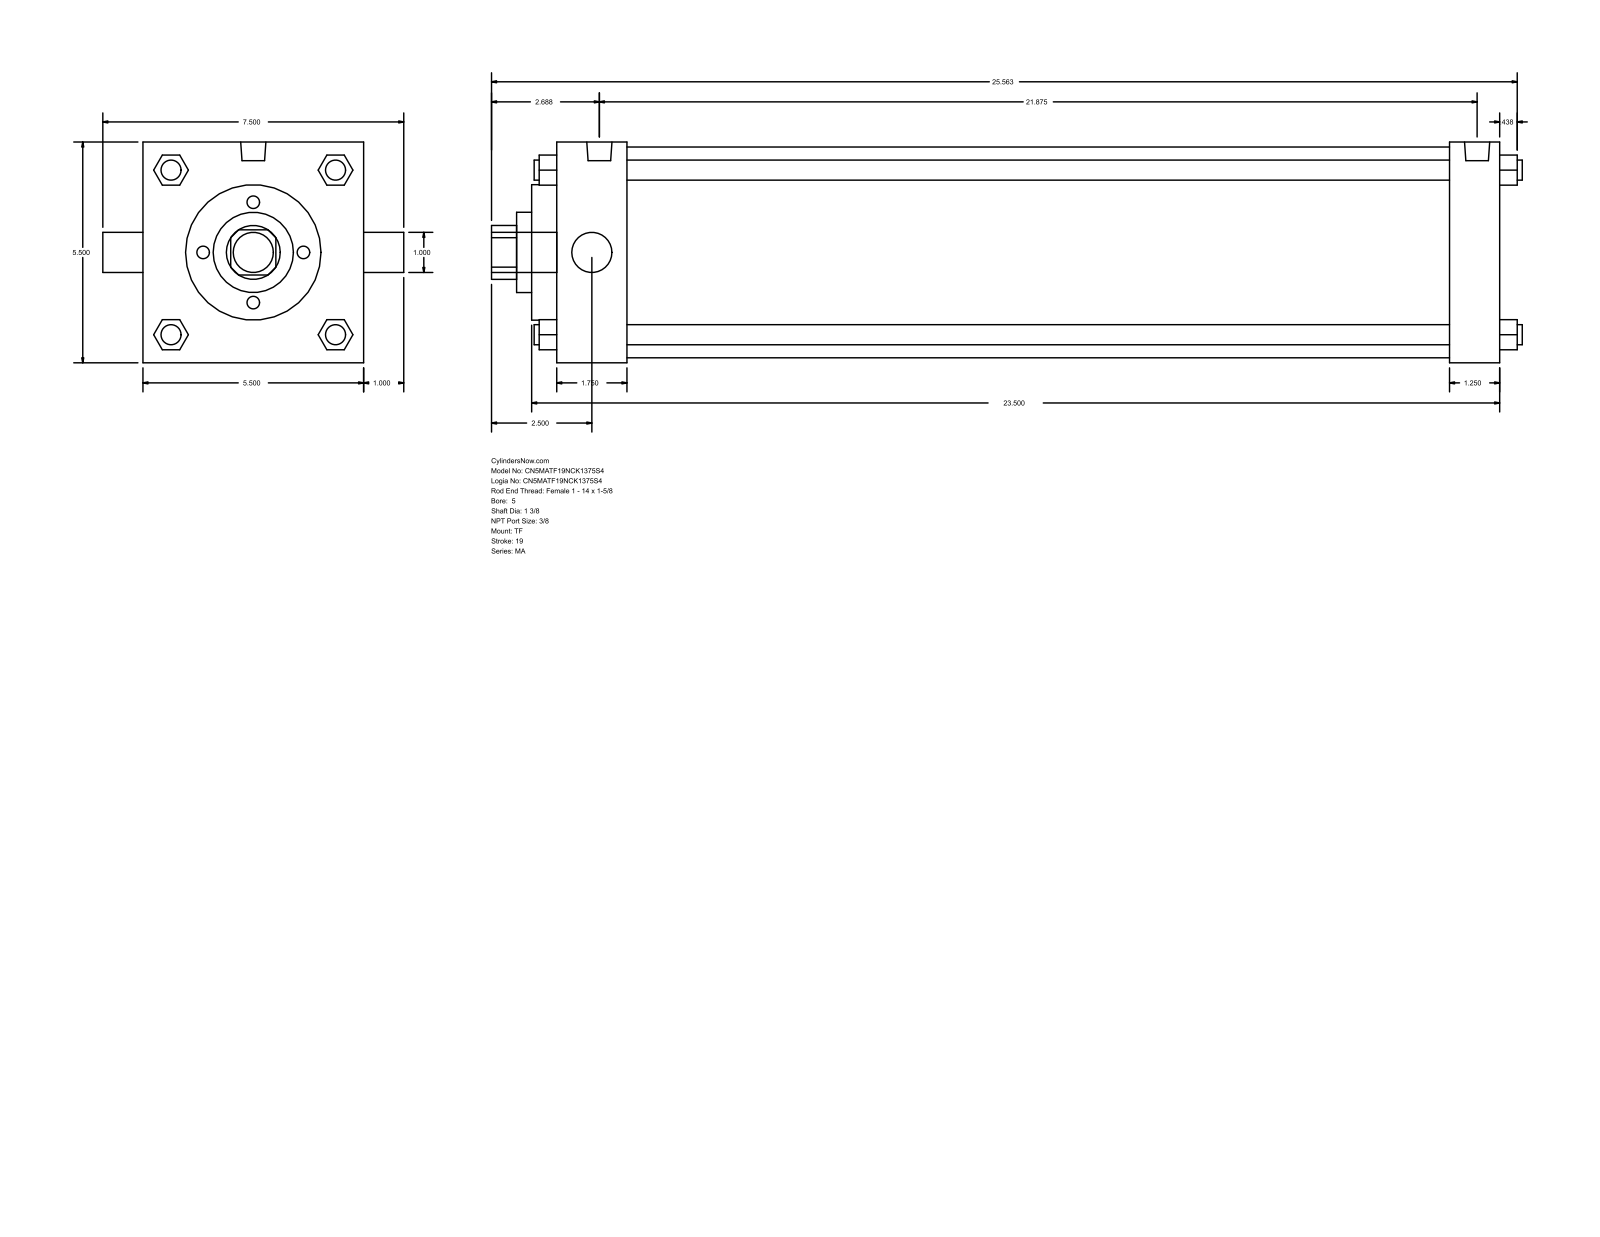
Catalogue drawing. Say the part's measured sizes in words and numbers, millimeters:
The part is named "MA_TF__0500_1.375". Its 3-D file was written by "GSSL Pune (CONFIG_CONTROL_DESIGN)". It is 0 solids with 122 faces: 93 planar, 29 cylindrical and 0 other. Overall it measures 652.46 by 190.5 by 139.7 millimeters. Round holes: 1 of diameter 25.4, 1 of diameter 34.92, 1 of diameter 50.8, 1 of diameter 85.72, 1 of diameter 133.35. Round bosses or shafts: 4 of diameter 12.7, 3 of diameter 11.11, 2 of diameter 15.93, 1 of diameter 25.4. Partial cylindrical surfaces (rounded edges, fillets, slot ends): 1 of radius 17.06. The main face-to-face distances are 139.7, 596.9, 565.15, 31.75, 44.45, 520.7, 552.45, 15.87, 60.32, 581.02.
